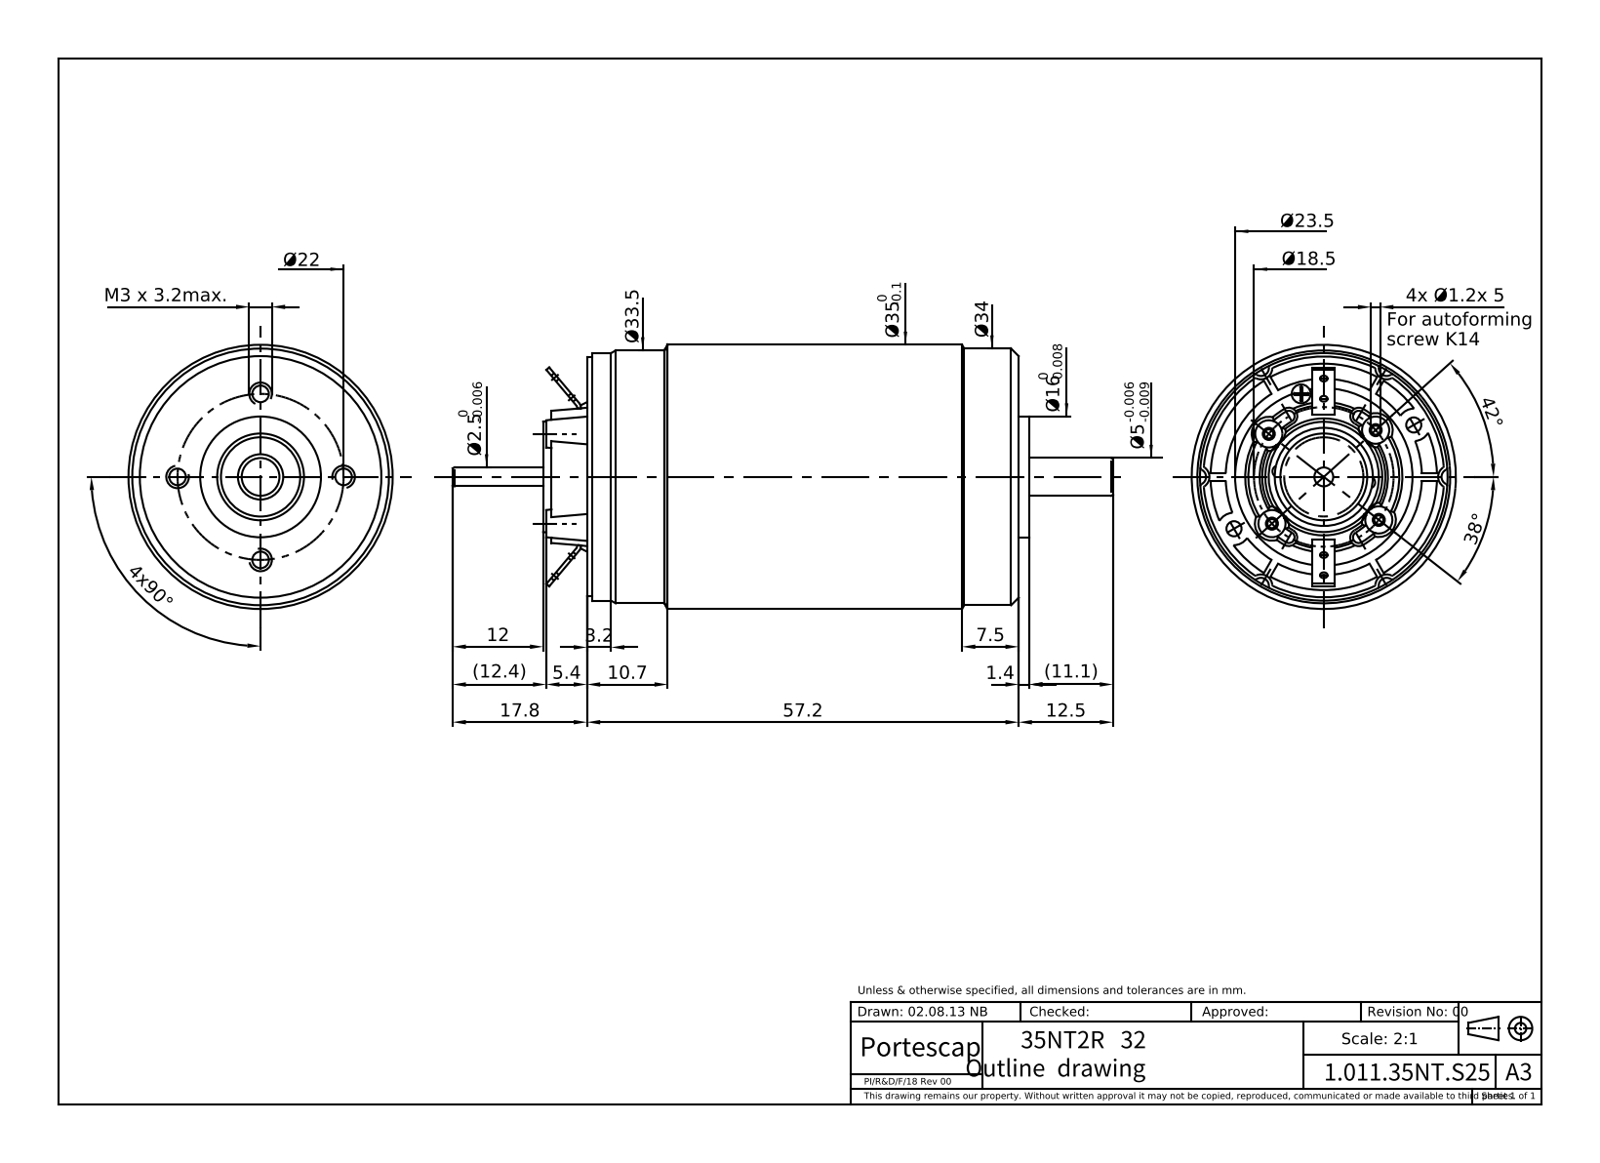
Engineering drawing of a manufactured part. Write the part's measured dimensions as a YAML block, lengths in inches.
part_name: "35NT2R"
step_written_by: "PRO/ENGINEER BY PARAMETRIC TECHNOLOGY CORPORATION, 2014310 (CONFIG_CONTROL_DESIGN)"
units: inches
bodies: {solids: 1, faces: 229, planar: 82, cylindrical: 87, other: 60}
overall_size: [2.995, 1.378, 1.378]
volume: 3.347
surface_area: 14.61
round_holes:
  - {diameter: 0.063, count: 6}
  - {diameter: 0.098, count: 5}
  - {diameter: 0.039, count: 4}
  - {diameter: 0.047, count: 4}
  - {diameter: 0.079, count: 2}
  - {diameter: 0.197, count: 1}
  - {diameter: 0.512, count: 1}
round_bosses_or_shafts:
  - {diameter: 1.378, count: 1}
  - {diameter: 1.339, count: 1}
  - {diameter: 1.319, count: 1}
  - {diameter: 1.291, count: 1}
  - {diameter: 1.252, count: 1}
  - {diameter: 0.63, count: 1}
partial_cylinders:
  - {radius: 0.083, count: 6}
  - {radius: 0.008, count: 4}
  - {radius: 0.394, count: 4}
  - {radius: 0.085, count: 2}
  - {radius: 0.024, count: 1}
face_to_face_distances: [0.02, 2.252, 2.232, 0.055, 2.287, 2.307, 2.345, 2.29, 0.057, 0.038]
hole_center_spacings: [0.364, 0.433, 0.613, 0.729, 0.138, 0.199, 0.217, 0.221]
